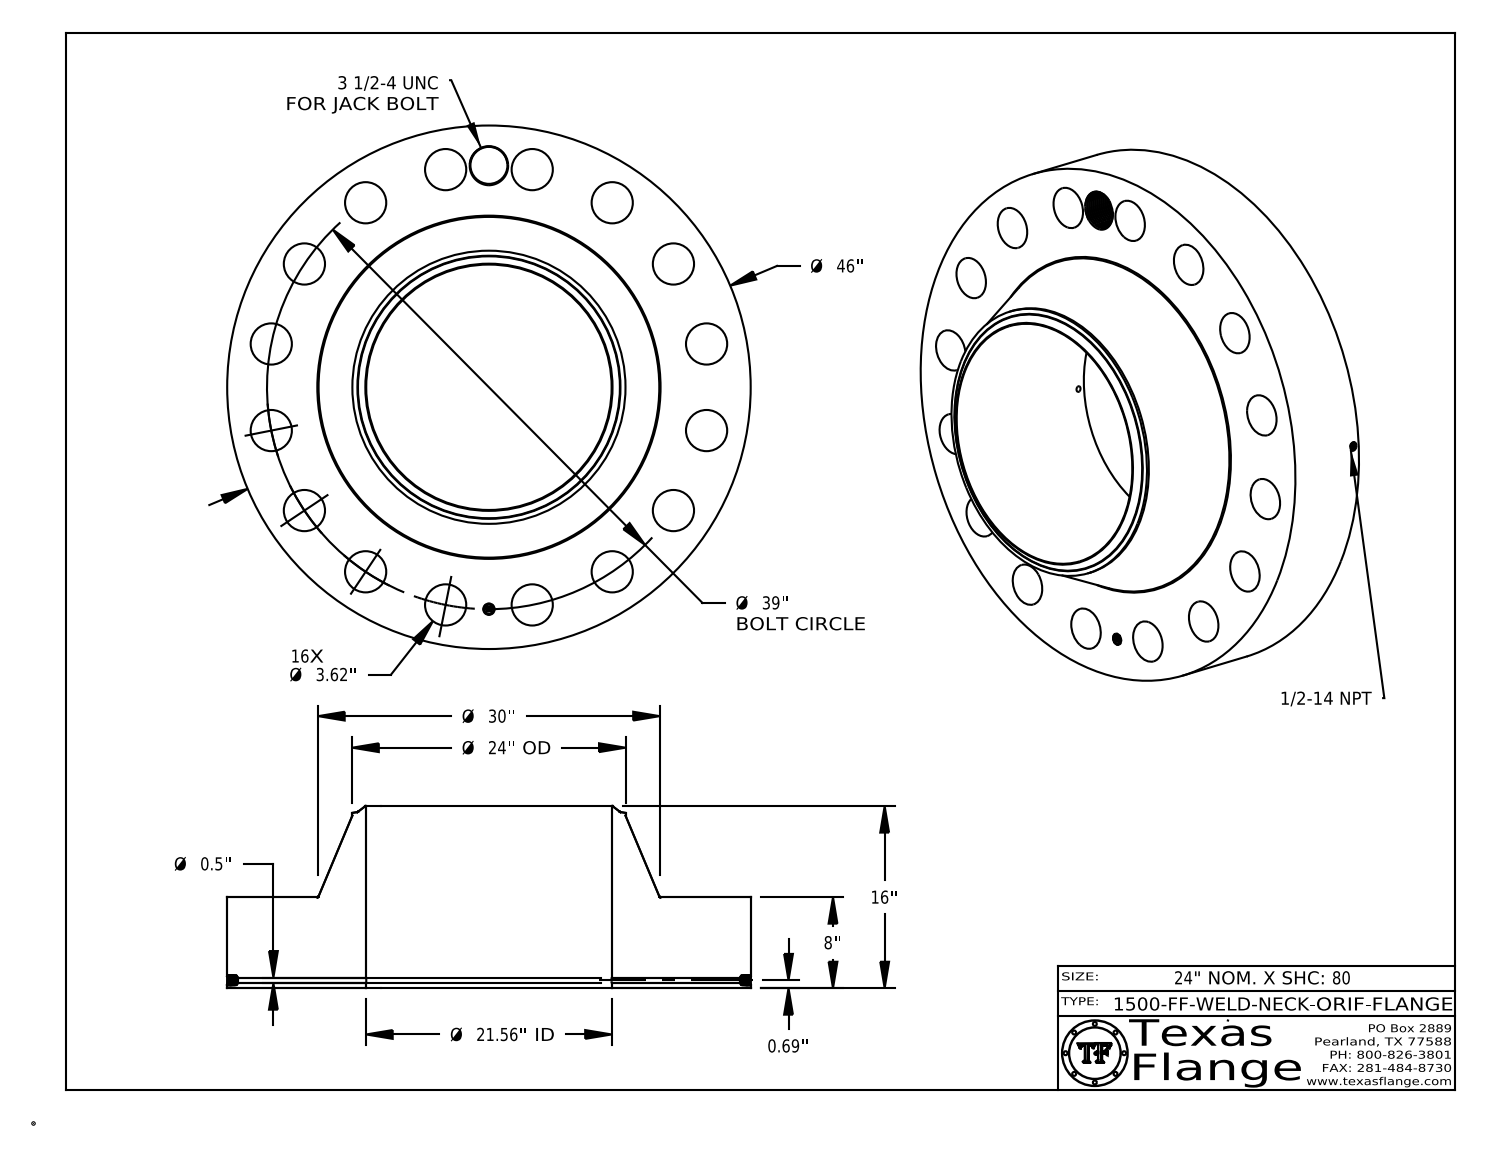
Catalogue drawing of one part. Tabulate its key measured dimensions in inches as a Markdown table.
| quantity | value |
| --- | --- |
| part name | 1500-FF-WELD-NECK |
| STEP written by | CATIA V5 STEP AP214 (AUTOMOTIVE_DESIGN) |
| units | inches |
| bodies | 1 solid, 888 faces (368 planar, 142 cylindrical, 378 other) |
| overall size | 46 × 46 × 16 |
| volume | 10 525 in³ |
| surface area | 6 537 in² |
| round holes (diameter × count) | 3.62 × 16, 0.5 × 1, 0.672 × 1, 1 × 1, 3.25 × 1, 21.562 × 1 |
| round bosses / shafts (diameter × count) | 0.061 × 8, 46 × 1, 24 × 1, 0.788 × 1 |
| main face-to-face distances | 8, 16, 7.985, 0.015, 8.015, 0.298, 0.293, 0.054, 0.248, 0.193 |
| hole center spacings | 19.5, 27.577, 36.031, 32.427, 7.608, 14.924, 14.925, 21.667 |
